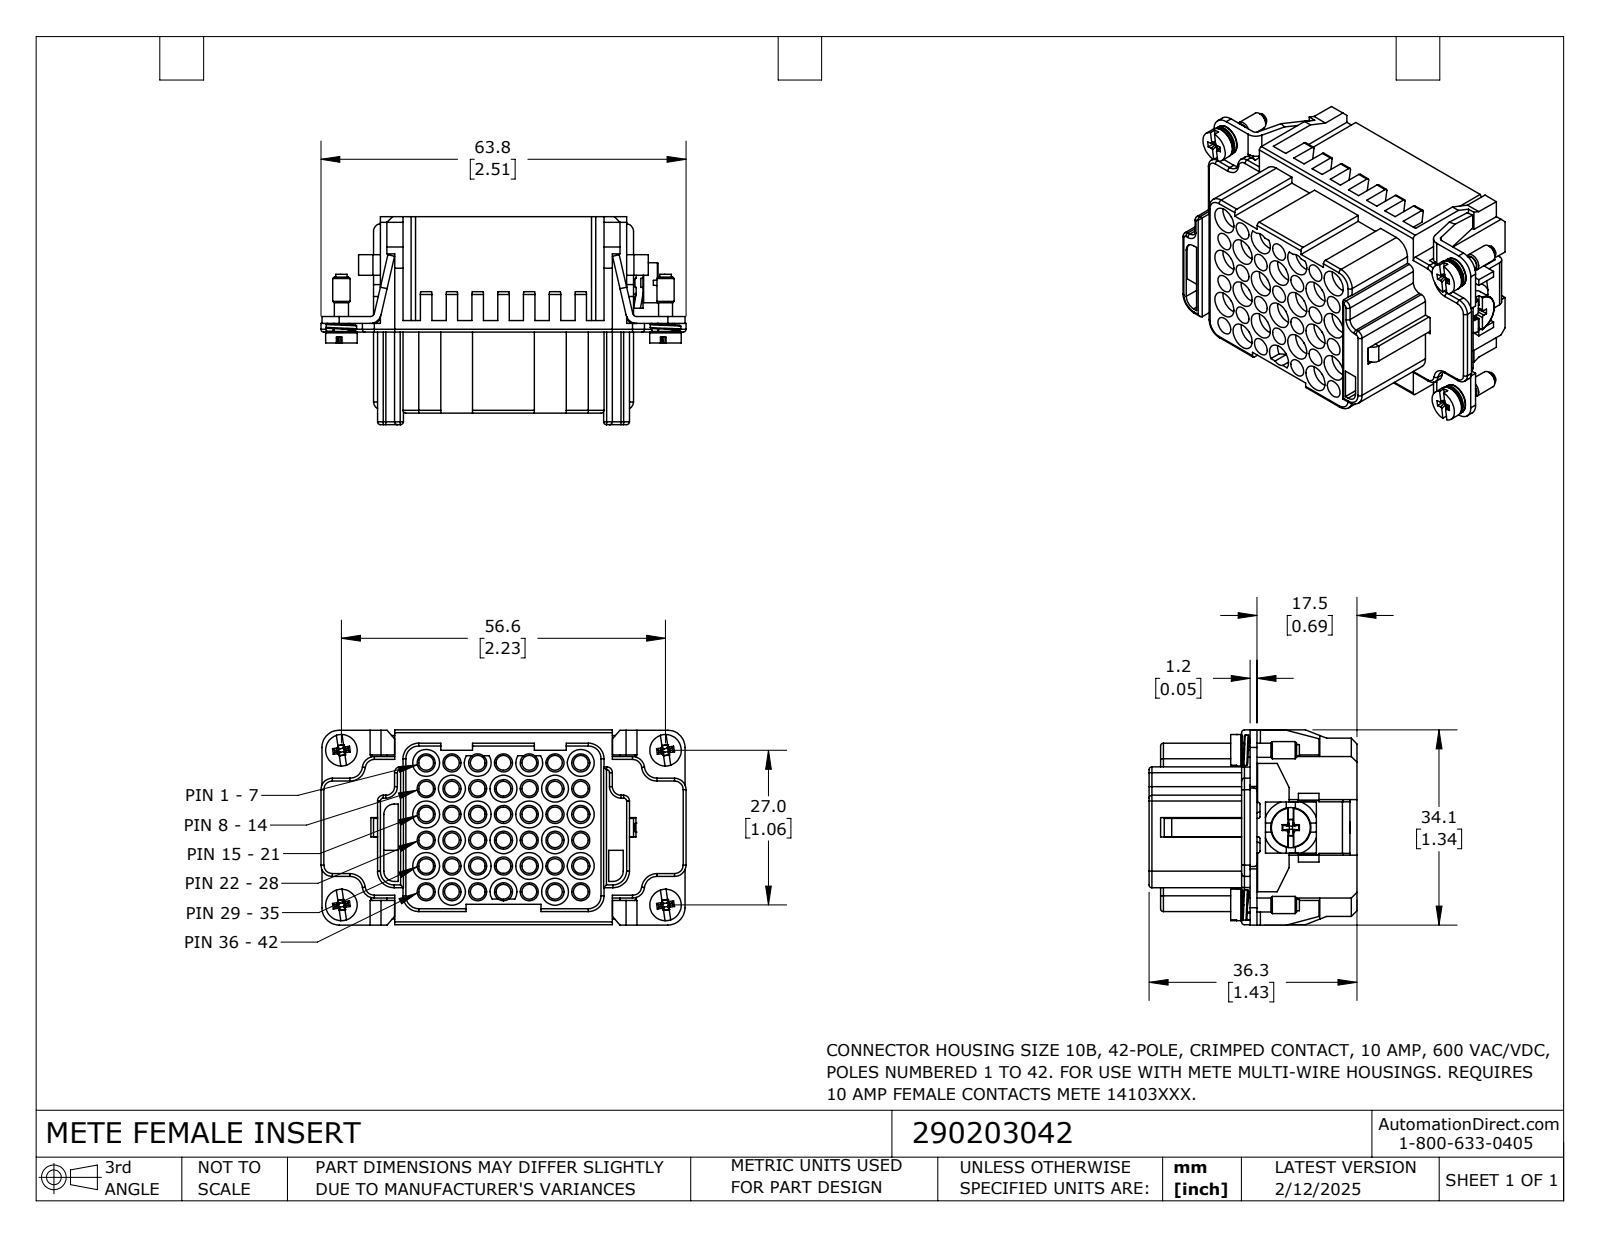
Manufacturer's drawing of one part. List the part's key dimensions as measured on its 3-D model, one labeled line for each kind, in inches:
Part name (STEP PRODUCT): 290203042
STEP written by: SolidWorks 2024 (CONFIG_CONTROL_DESIGN)
Units: inches
Bodies: 13 solids, 1523 faces (740 planar, 648 cylindrical, 135 other)
Overall size (bounding box): 2.51 × 1.429 × 1.341
Volume: 1.672 in³ · Surface area: 48.65 in²
Round holes (diameter × count): ⌀0.102 ×42, ⌀0.124 ×42, ⌀0.138 ×42, ⌀0.15 ×42, ⌀0.185 ×18, ⌀0.114 ×4, ⌀0.142 ×2, ⌀0.13 ×1
Round bosses / shafts (diameter × count): ⌀0.217 ×4, ⌀0.209 ×4, ⌀0.118 ×4, ⌀0.096 ×4, ⌀0.079 ×4, ⌀0.126 ×2, ⌀0.276 ×1, ⌀0.201 ×1
Partial cylindrical surfaces — rounded edges, fillets, slot ends (radius × count): R0.02 ×33, R0.01 ×32, R0.012 ×12, R0.004 ×10, R0.051 ×10, R0.006 ×8, R0.053 ×8, R0.014 ×4
Main face-to-face distances: 0.047, 0.098, 1.516, 0.079, 0.177, 0.02, 1.614, 0.687, 0.028, 0.024
Hole centre spacings: 0.396, 0.56, 0.25, 0.177, 0.354, 0.639, 0.73, 0.501
